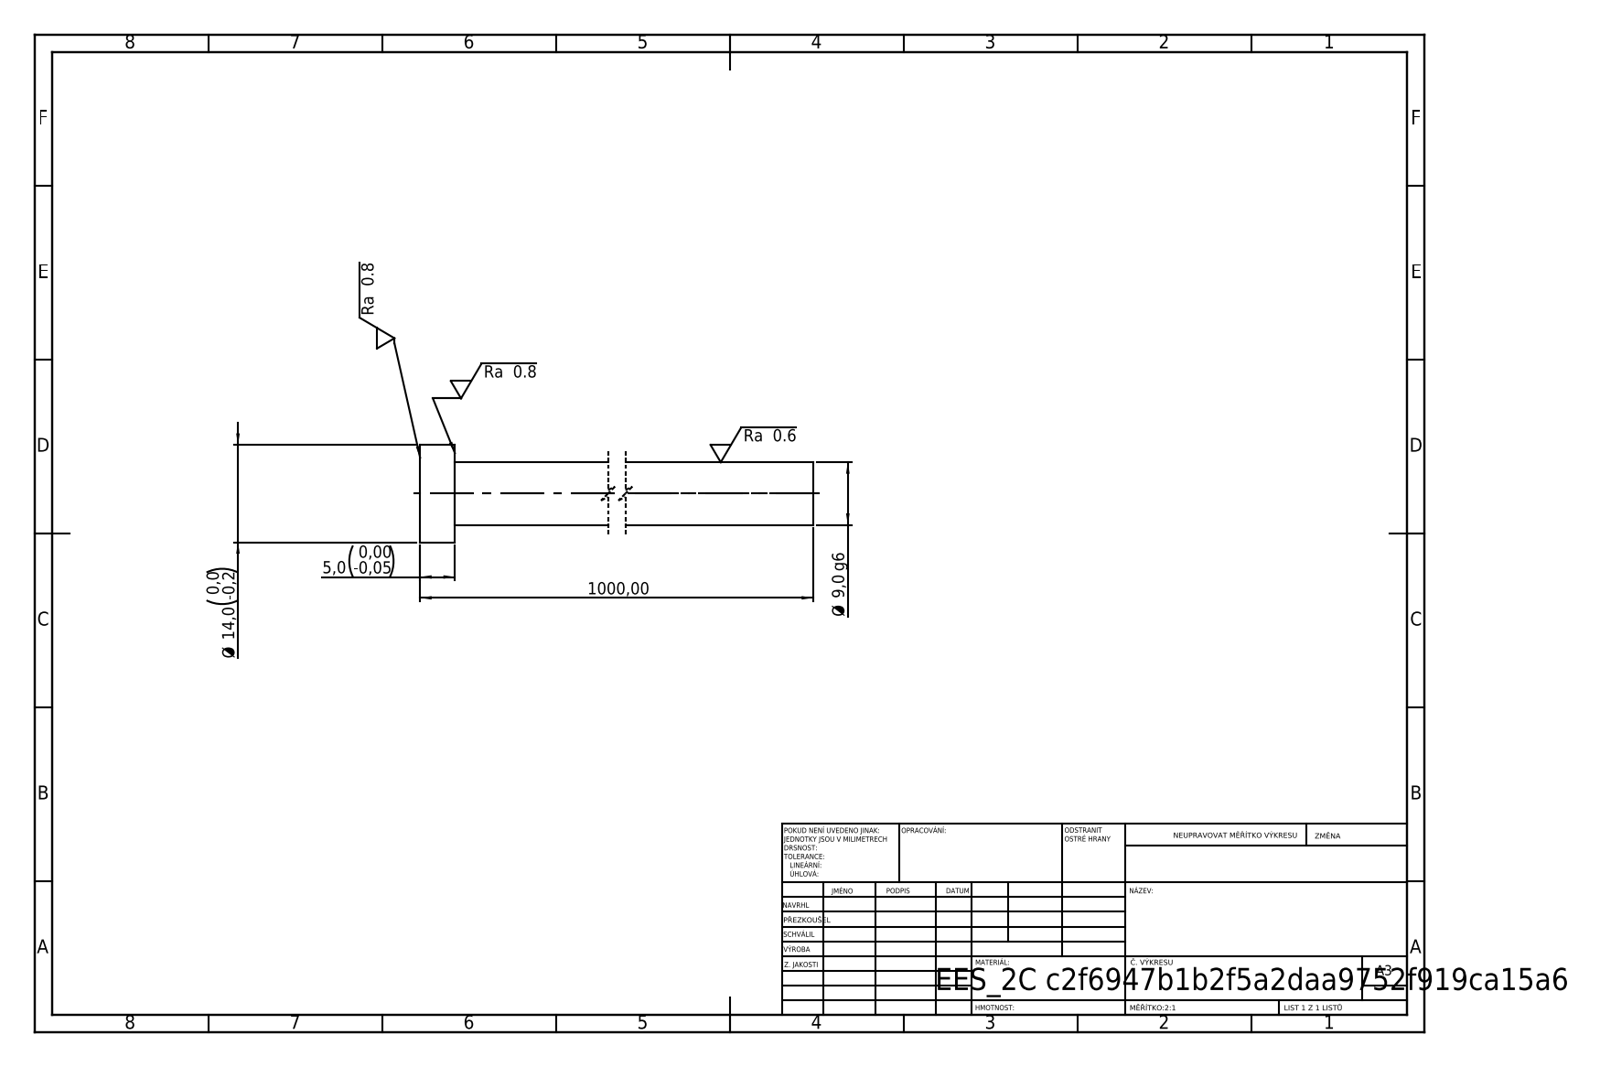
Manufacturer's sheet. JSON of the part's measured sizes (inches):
{"step_written_by": "SolidWorks 2019 (CONFIG_CONTROL_DESIGN)", "units": "inches", "bodies": {"solids": 1, "faces": 7, "planar": 3, "cylindrical": 4, "other": 0}, "overall_size": [39.37, 0.551, 0.551], "volume_in3": 3.91, "surface_area_in2": 44.42, "round_bosses_or_shafts": [[0.551, 1], [0.354, 1]], "face_to_face_distances": [0.197, 39.37, 39.173]}
